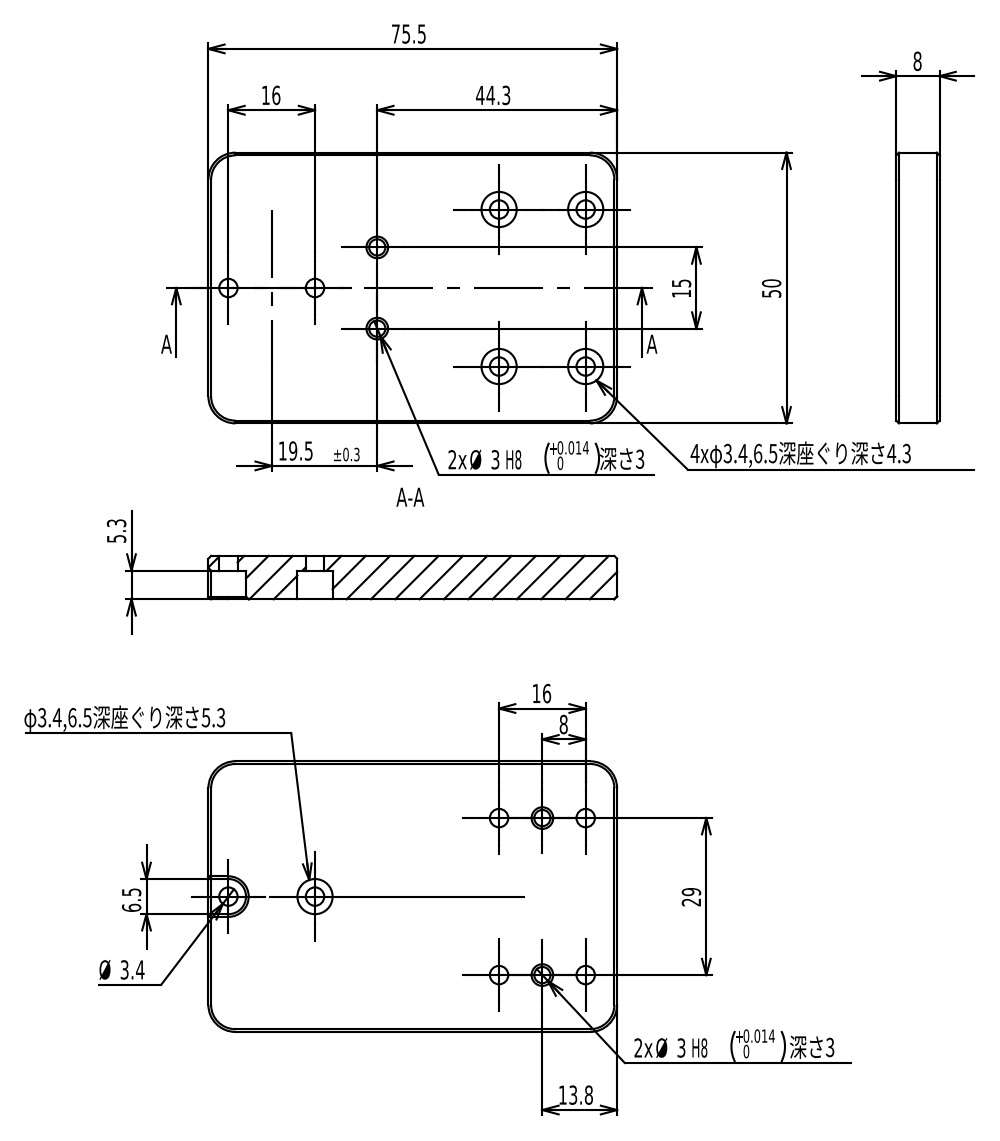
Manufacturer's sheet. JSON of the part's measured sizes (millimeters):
{"part_name": "PDG60-3-1", "step_written_by": "SolidWorks 2020 (CONFIG_CONTROL_DESIGN)", "units": "millimeters", "bodies": {"solids": 1, "faces": 86, "planar": 34, "cylindrical": 35, "other": 17}, "overall_size": [75.5, 50, 8], "volume_mm3": 28729, "surface_area_mm2": 10024, "round_holes": [[3.4, 6], [6.5, 5], [3, 4]], "partial_cylinders_radius": [[5, 4], [3.25, 1]], "face_to_face_distances": [8, 50, 75.5, 3.7, 4.3, 40.3, 5.3, 1.6, 2.7, 21.75], "hole_center_spacings": [8, 30.08, 52.06, 16, 29, 13.73, 23.56, 28.5]}
